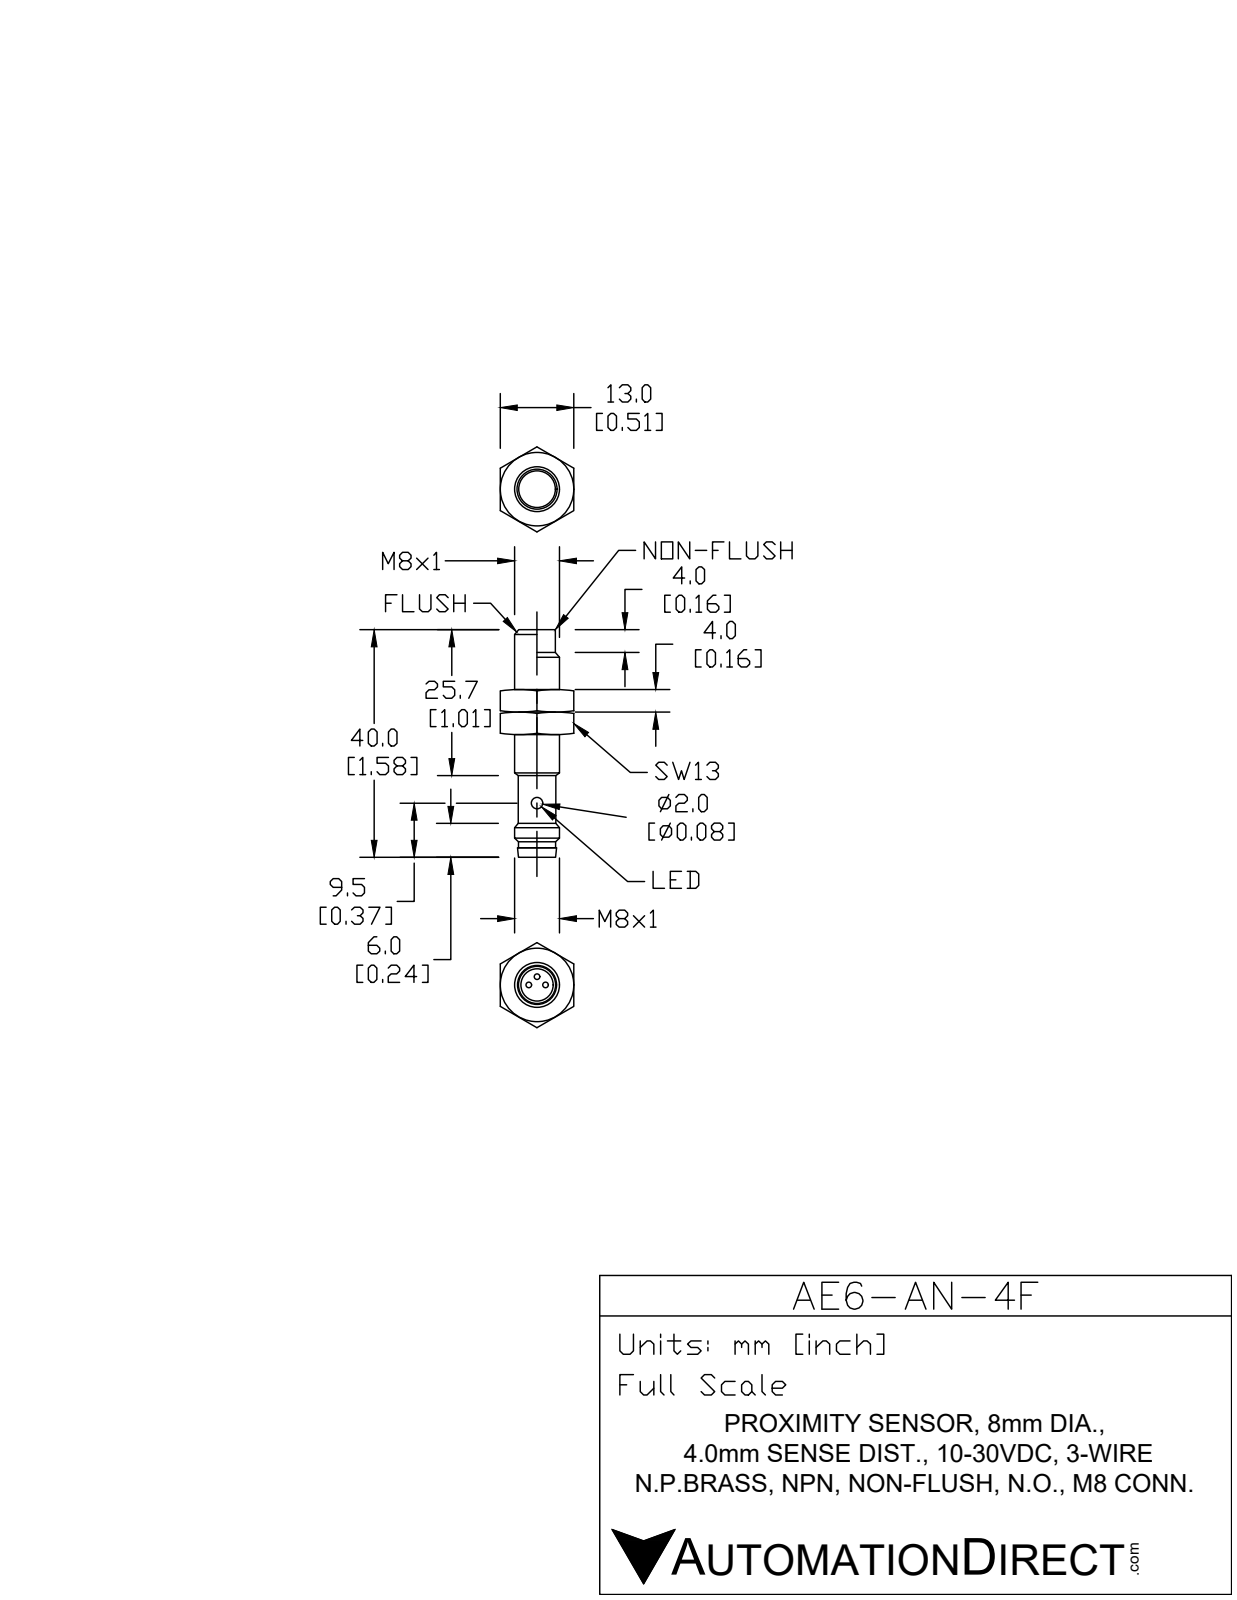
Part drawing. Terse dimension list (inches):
name: AE6-AN-4F
written by: SolidWorks 2017 (AUTOMOTIVE_DESIGN)
unit: in
bodies: 3 solids, 61 faces (11 planar, 30 cylindrical, 20 other)
size: 1.575 × 0.315 × 0.315
volume: 0.103 in³; area: 2.261 in²
holes: 4× ⌀0.079, 1× ⌀0.228
bosses: 3× ⌀0.039, 1× ⌀0.315, 1× ⌀0.272, 1× ⌀0.256, 1× ⌀0.23
face distances: 0.157, 1.122, 0.965, 1.26, 1.102, 0.138, 1.378, 1.22, 0.256, 0.118
